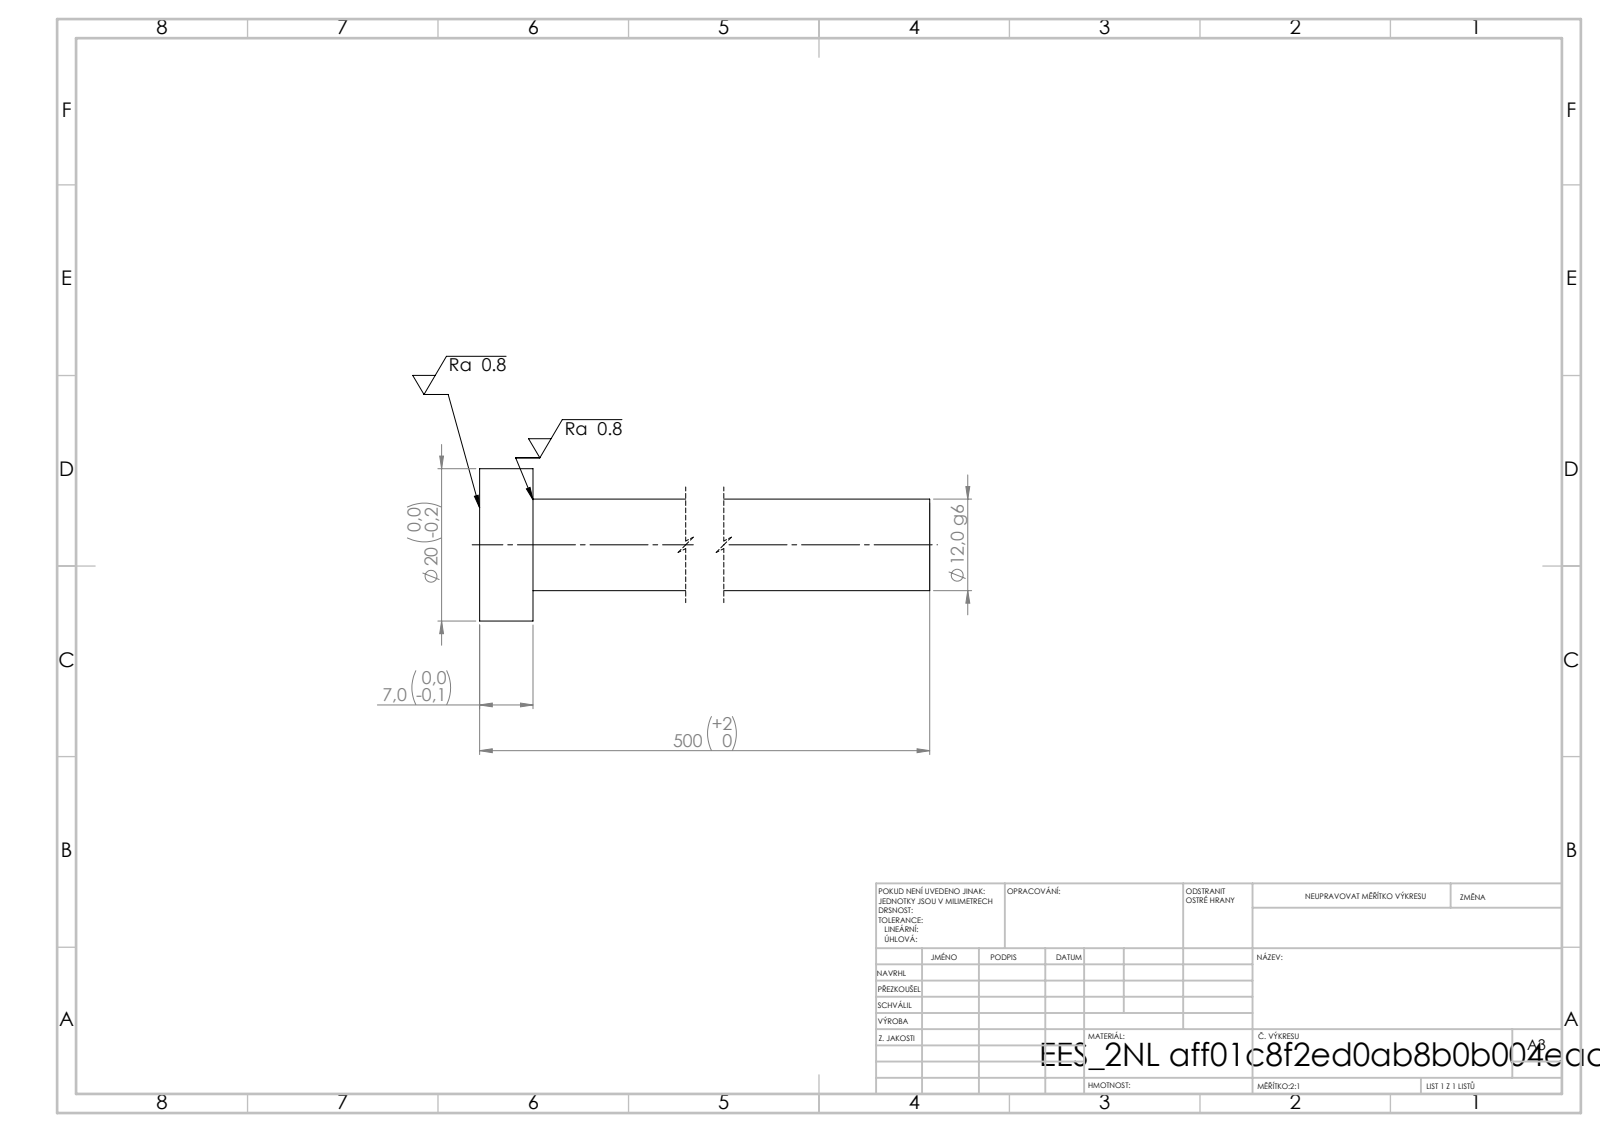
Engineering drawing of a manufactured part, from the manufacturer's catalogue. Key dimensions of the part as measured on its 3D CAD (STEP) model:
STEP written by: SolidWorks 2019 (CONFIG_CONTROL_DESIGN)
Units: millimetres
Bodies: 1 solid, 7 faces (3 planar, 4 cylindrical, 0 other)
Overall size (bounding box): 500 × 20 × 20
Volume: 57 956 mm³ · Surface area: 19 654 mm²
Round bosses / shafts (diameter × count): ⌀20 ×1, ⌀12 ×1
Main face-to-face distances: 7, 500, 493
